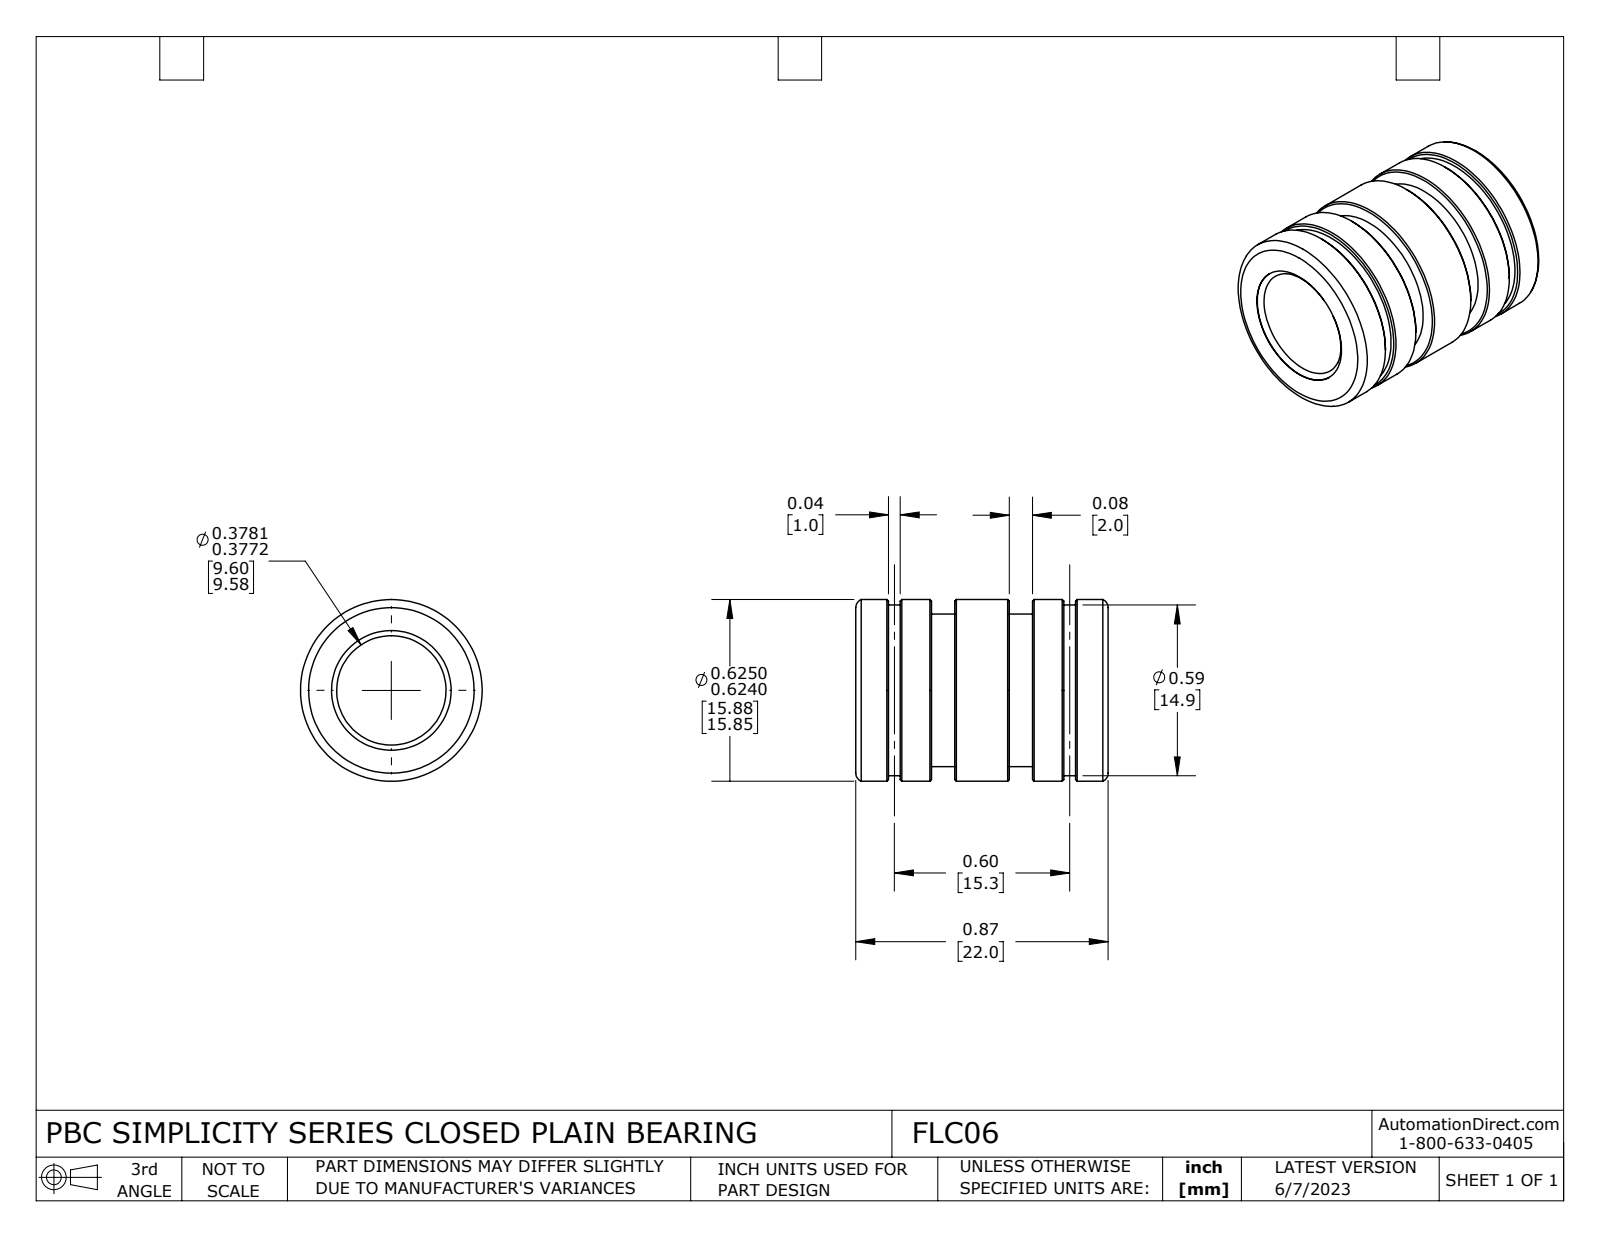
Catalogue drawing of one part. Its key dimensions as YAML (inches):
part_name: "FLC06"
step_written_by: "SolidWorks 2021 (CONFIG_CONTROL_DESIGN)"
units: inches
bodies: {solids: 2, faces: 58, planar: 10, cylindrical: 24, other: 24}
overall_size: [0.868, 0.624, 0.624]
volume: 0.151
surface_area: 5.677
round_holes:
  - {diameter: 0.376, count: 1}
  - {diameter: 0.411, count: 1}
round_bosses_or_shafts:
  - {diameter: 0.624, count: 1}
  - {diameter: 0.587, count: 1}
  - {diameter: 0.524, count: 1}
face_to_face_distances: [0.26, 0.341, 0.527, 0.607, 0.08, 0.267, 0.868, 0.347, 0.187, 0.153]
